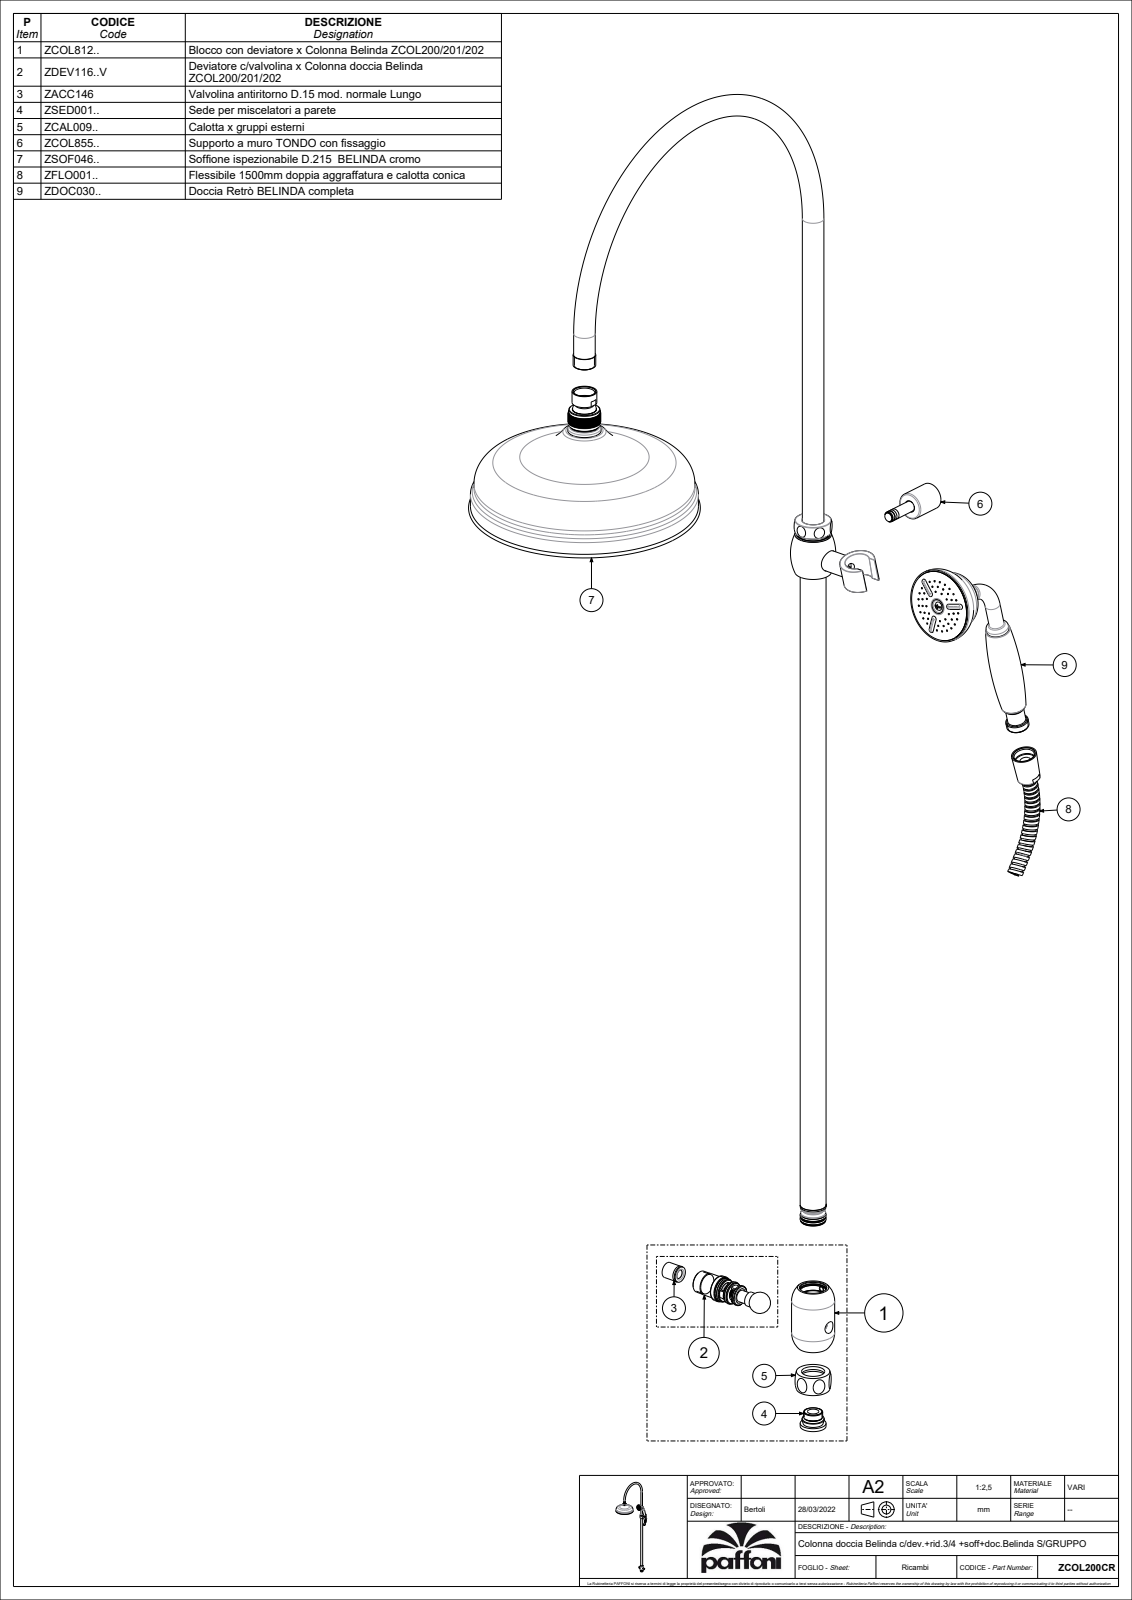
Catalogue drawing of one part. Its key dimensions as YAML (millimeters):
part_name: "ZCOL200CR"
step_written_by: "CREO PARAMETRIC BY PTC INC, 2021404 (CONFIG_CONTROL_DESIGN)"
units: millimeters
bodies: {solids: 6, faces: 2361, planar: 940, cylindrical: 704, other: 717}
overall_size: [1263, 512, 215]
volume: 1742000
surface_area: 426571
round_holes:
  - {diameter: 2, count: 100}
  - {diameter: 1.2, count: 45}
  - {diameter: 5, count: 5}
  - {diameter: 10.5, count: 3}
  - {diameter: 13, count: 3}
  - {diameter: 3, count: 2}
  - {diameter: 4.2, count: 2}
  - {diameter: 8.5, count: 2}
  - {diameter: 10, count: 2}
  - {diameter: 12.2, count: 2}
  - {diameter: 14.5, count: 2}
  - {diameter: 17, count: 2}
round_bosses_or_shafts:
  - {diameter: 21, count: 4}
  - {diameter: 28, count: 2}
  - {diameter: 24, count: 2}
  - {diameter: 22, count: 2}
  - {diameter: 20.5, count: 2}
  - {diameter: 20, count: 2}
  - {diameter: 14, count: 2}
  - {diameter: 211.5, count: 1}
partial_cylinders:
  - {radius: 0.5, count: 14}
  - {radius: 0.3, count: 6}
  - {radius: 5.25, count: 1}
  - {radius: 6.75, count: 1}
  - {radius: 9.75, count: 1}
  - {radius: 15, count: 1}
face_to_face_distances: [15, 1, 7, 2, 41, 27.5, 709, 32, 11, 0.5]
hole_center_spacings: [24, 23.99, 18.99, 14, 19, 14.01, 57, 11.08]
